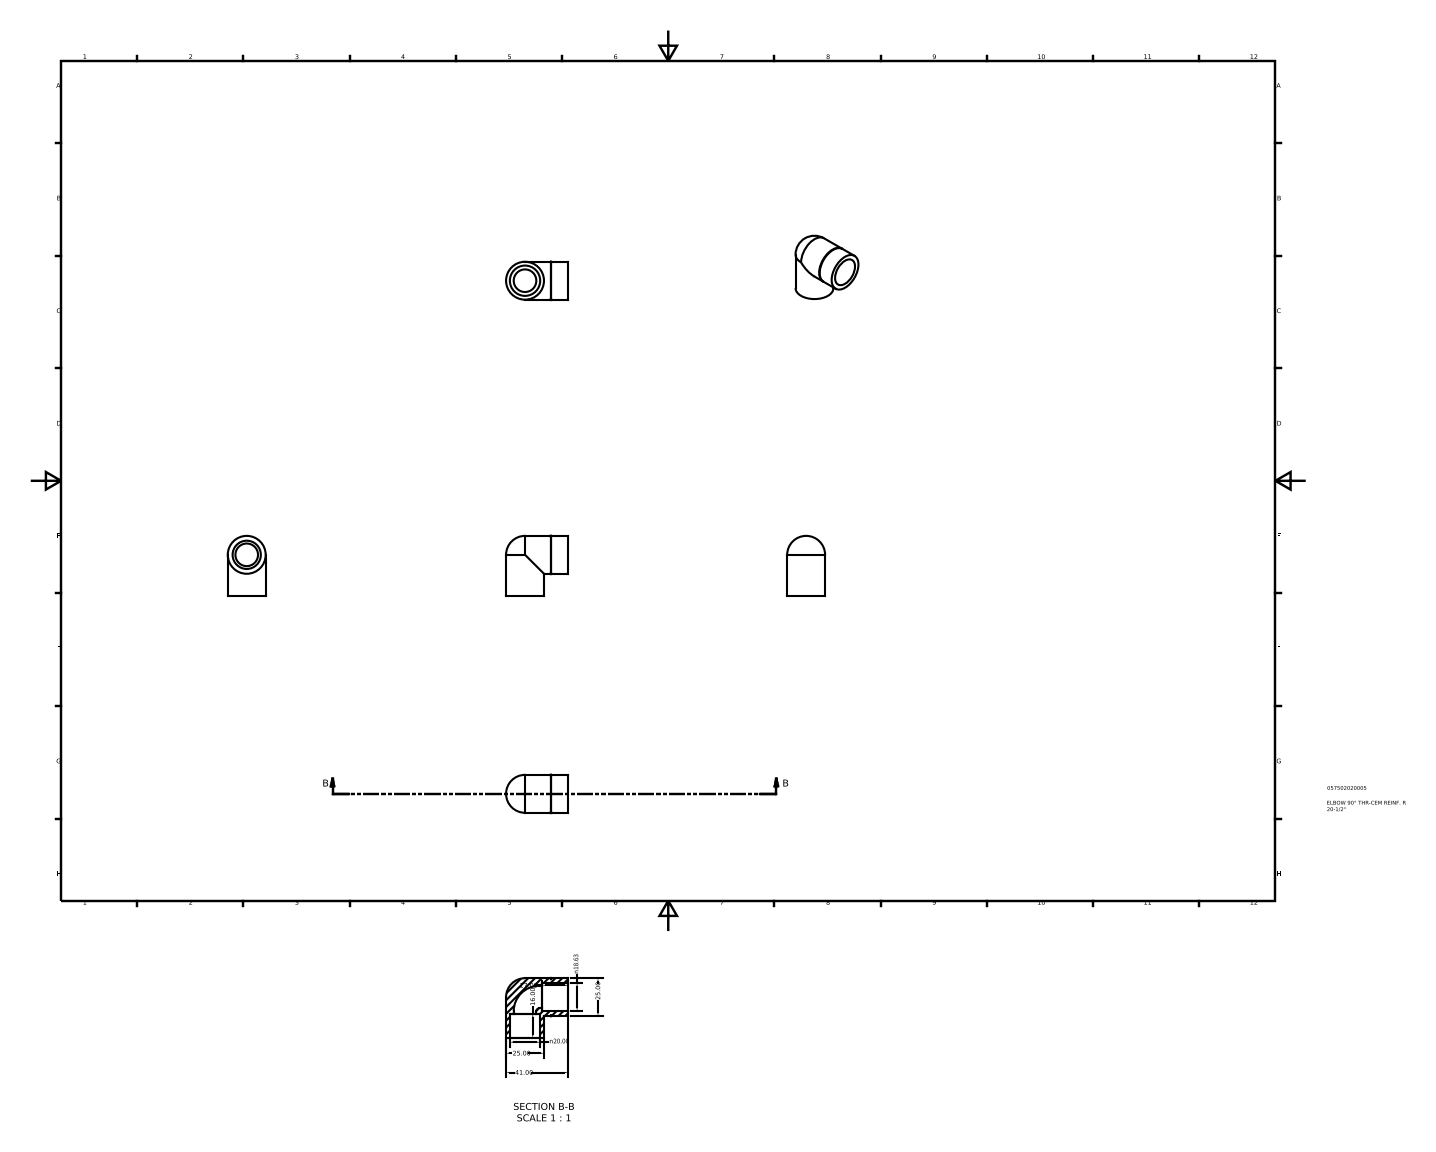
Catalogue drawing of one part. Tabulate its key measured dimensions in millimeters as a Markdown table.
| quantity | value |
| --- | --- |
| part name | 057502020005 |
| STEP written by | Autodesk Inventor 2015 (AUTOMOTIVE_DESIGN) |
| units | millimeters |
| bodies | 1 solid, 15 faces (4 planar, 7 cylindrical, 4 other) |
| overall size | 41 × 39.5 × 25 |
| volume | 13 786 mm³ |
| surface area | 7 771 mm² |
| round holes (diameter × count) | 14.9 × 2, 18.63 × 1, 20 × 1 |
| round bosses / shafts (diameter × count) | 25 × 2 |
| main face-to-face distances | 16, 17 |
